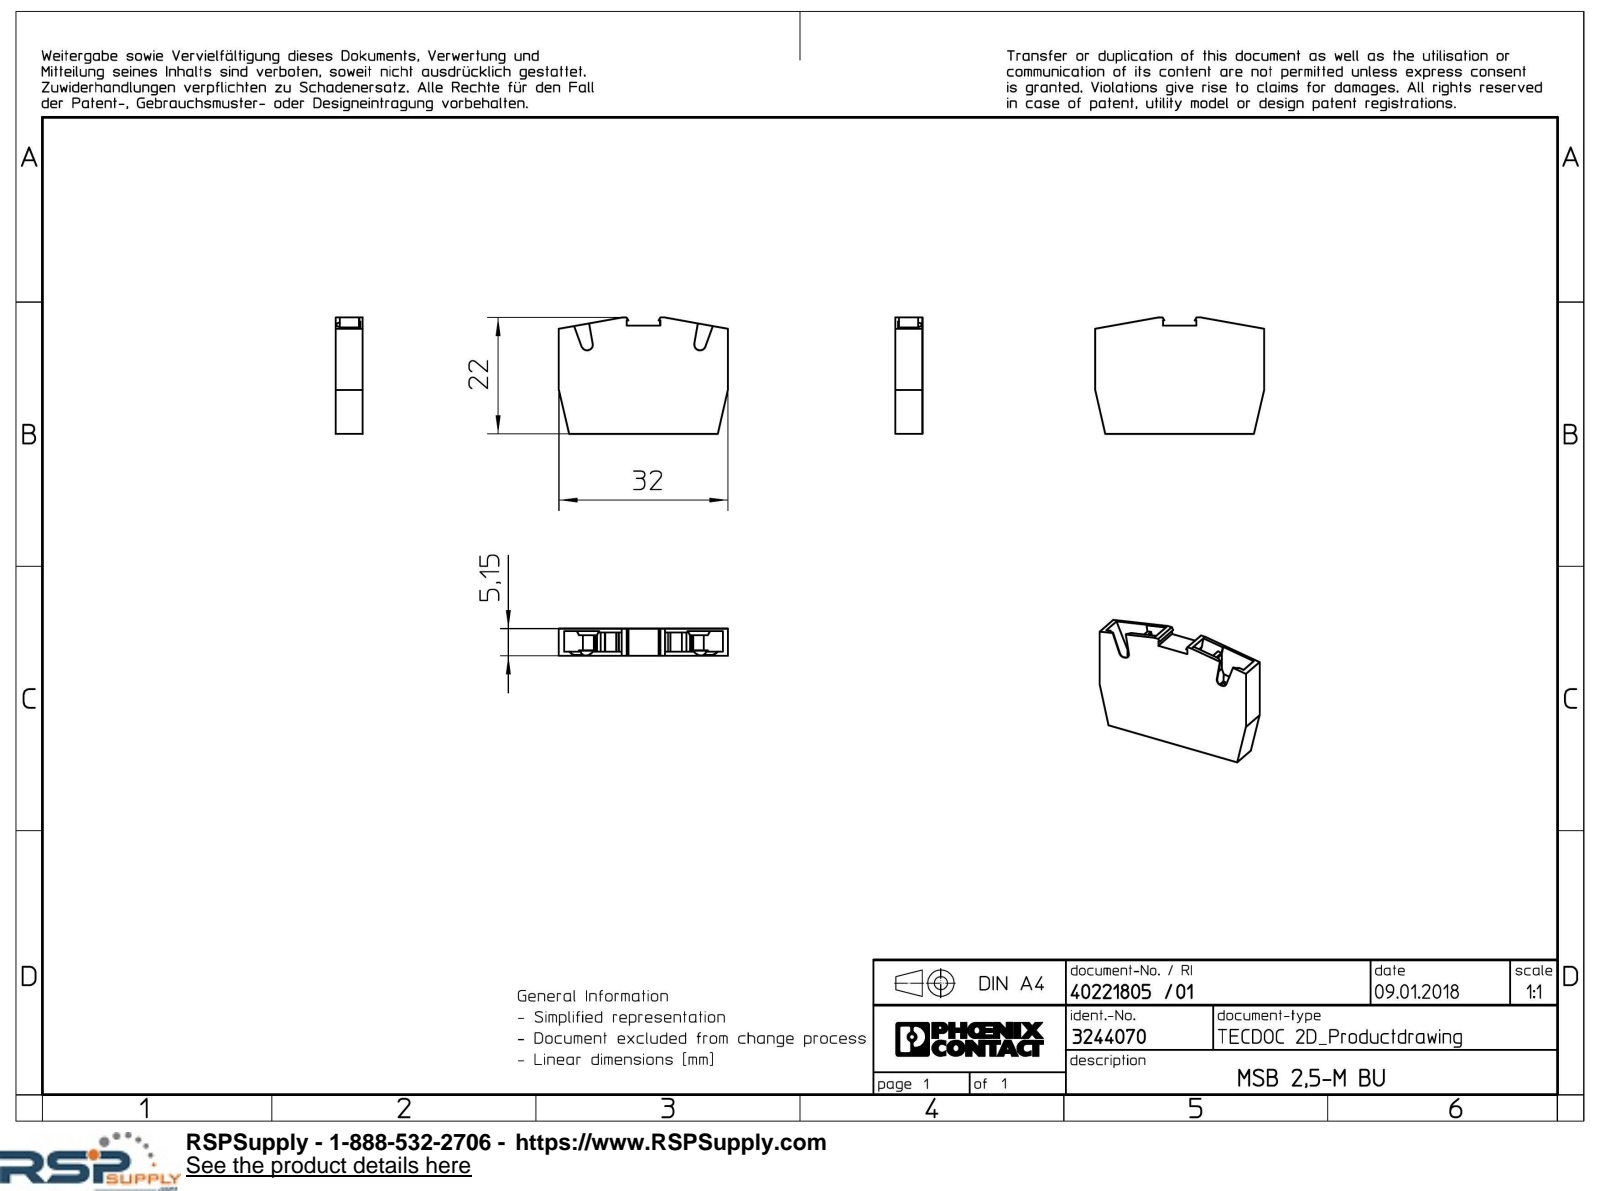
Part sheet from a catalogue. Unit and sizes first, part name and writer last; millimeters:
Units: millimetres
Overall size (bounding box): 32 × 22 × 5.15
Partial cylindrical surfaces — rounded edges, fillets, slot ends (radius × count): R1 ×4, R1.2 ×4, R2.4 ×2, R2.62 ×2
Main face-to-face distances: 5.15, 3.65, 4.35, 0.8, 0.7, 4.45, 0.5, 3.85, 4.65, 32
Volume: 2 614 mm³ · Surface area: 2 549 mm²
Bodies: 1 solid, 92 faces (80 planar, 12 cylindrical, 0 other)
Part name (STEP PRODUCT): MSB_2.5_M_BU-select
STEP written by: Creo Elements/Direct Modeling 20.1A 29-Sep-2018 (C) Parametric Technology GmbH (AUTOMOTIVE_DESIGN)
